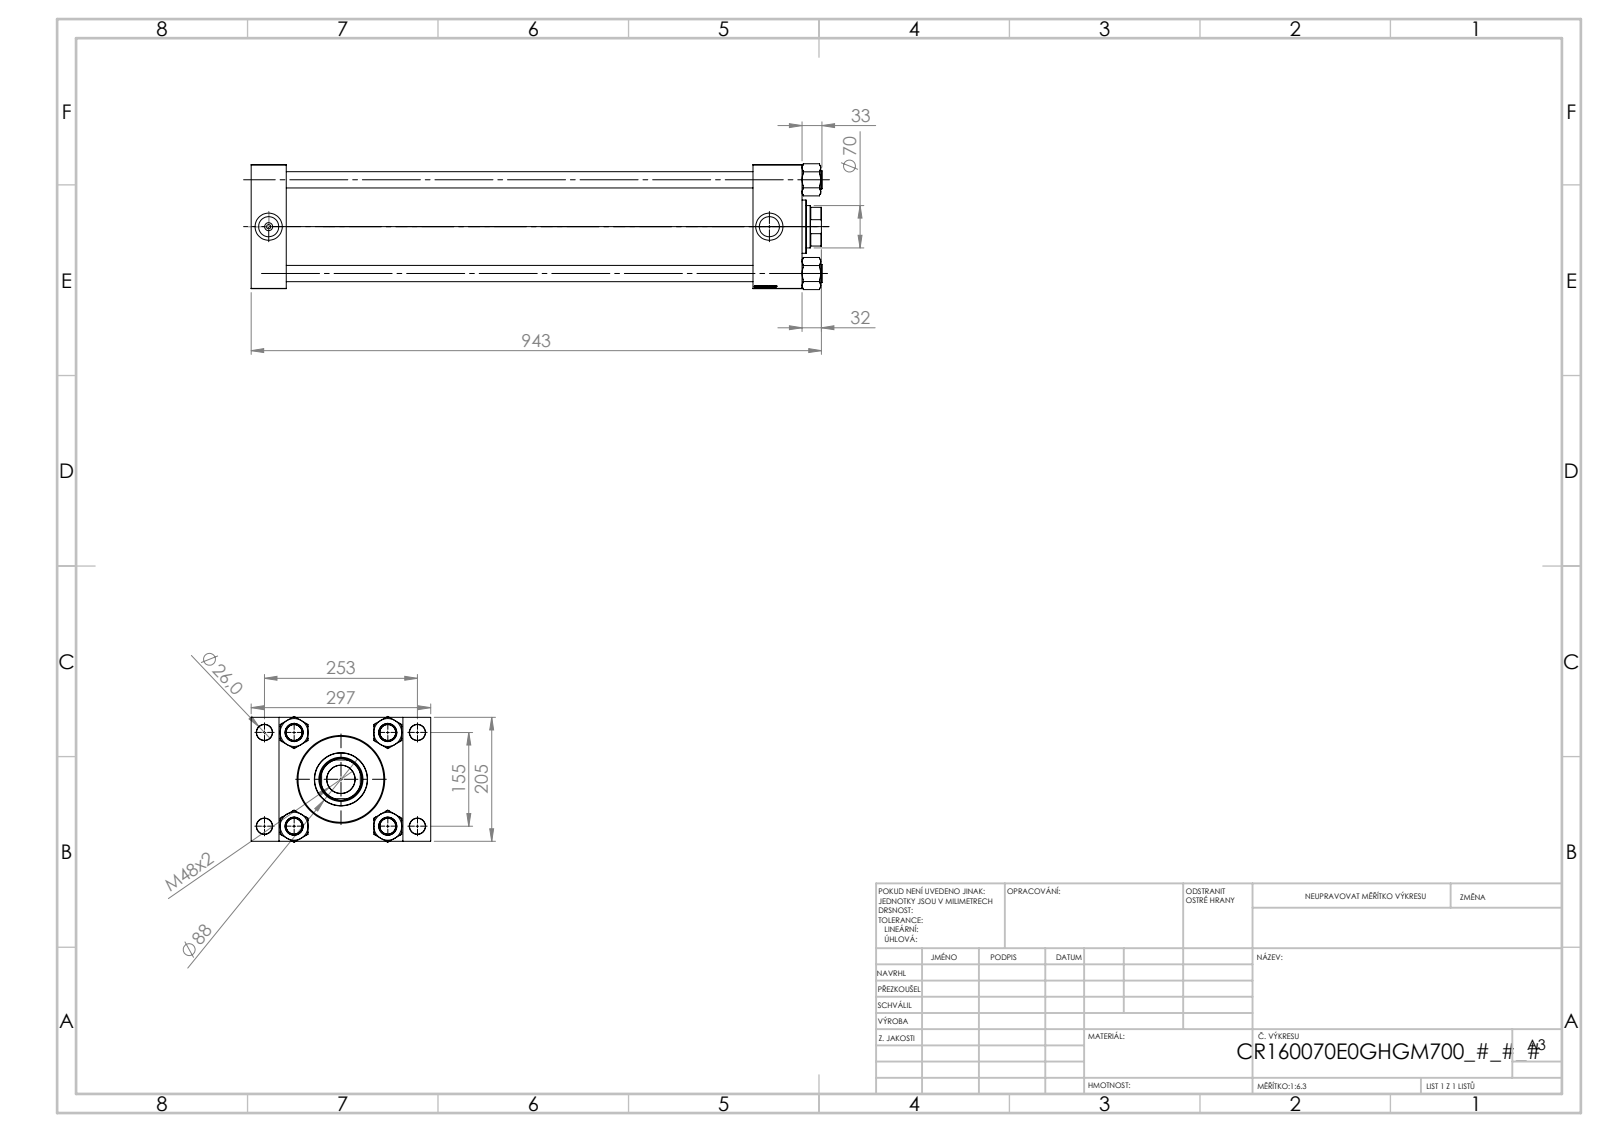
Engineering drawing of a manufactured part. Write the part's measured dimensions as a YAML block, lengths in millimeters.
part_name: "V215CR_E_Body; V215CR_TYCINKA_E; NUT_M5_E; V215_VC_A (+1 more)"
step_written_by: "SolidWorks 2019 (CONFIG_CONTROL_DESIGN)"
units: millimeters
bodies: {solids: 11, faces: 1190, planar: 548, cylindrical: 90, other: 552}
overall_size: [944, 297, 208.14]
volume: 13640000
surface_area: 1857000
round_holes:
  - {diameter: 26, count: 4}
  - {diameter: 27, count: 4}
  - {diameter: 2.5, count: 2}
  - {diameter: 7, count: 2}
  - {diameter: 33.24, count: 2}
  - {diameter: 45, count: 2}
  - {diameter: 46.5, count: 1}
  - {diameter: 70, count: 1}
  - {diameter: 73, count: 1}
  - {diameter: 120, count: 1}
  - {diameter: 142, count: 1}
  - {diameter: 160, count: 1}
round_bosses_or_shafts:
  - {diameter: 30, count: 4}
  - {diameter: 166, count: 1}
  - {diameter: 88, count: 1}
partial_cylinders:
  - {radius: 34, count: 1}
face_to_face_distances: [58, 205, 911, 853, 830, 772, 81, 46, 251, 882.3]
hole_center_spacings: [49.05, 77.88, 96.35, 109.53, 148.35, 154.9, 162.53, 165.89]
